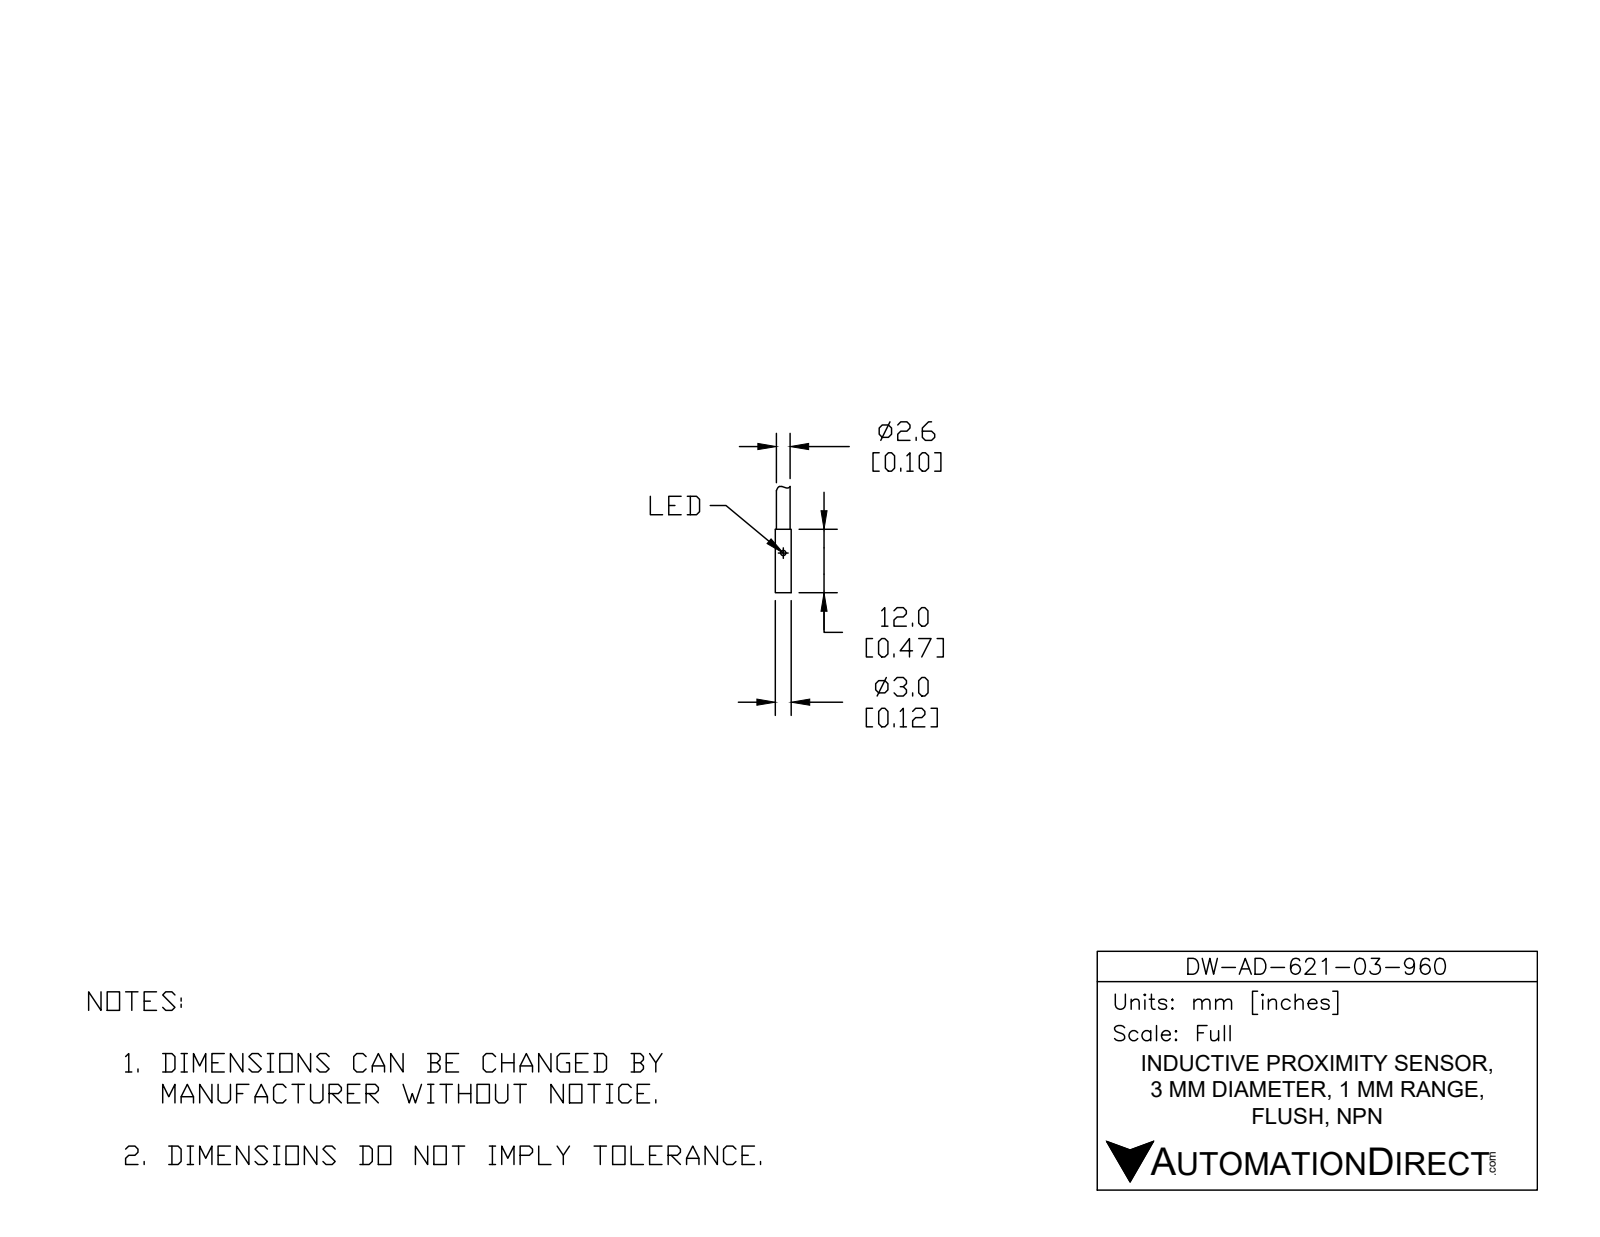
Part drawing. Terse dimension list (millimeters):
name: DW-AD-621-03-960
written by: SolidWorks 2021 (AUTOMOTIVE_DESIGN)
unit: mm
bodies: 1 solid, 21 faces (6 planar, 13 cylindrical, 2 other)
size: 20 × 3 × 3
volume: 124 mm³; area: 210 mm²
holes: 1× ⌀1, 1× ⌀2.7
bosses: 1× ⌀3, 1× ⌀2.65, 1× ⌀2.6
rounds: 1× R0.44, 1× R0.6, 1× R2.4, 1× R3.6, 1× R4.8
face distances: 12, 20, 8, 11, 1, 9, 10.9, 11.9, 19.9
